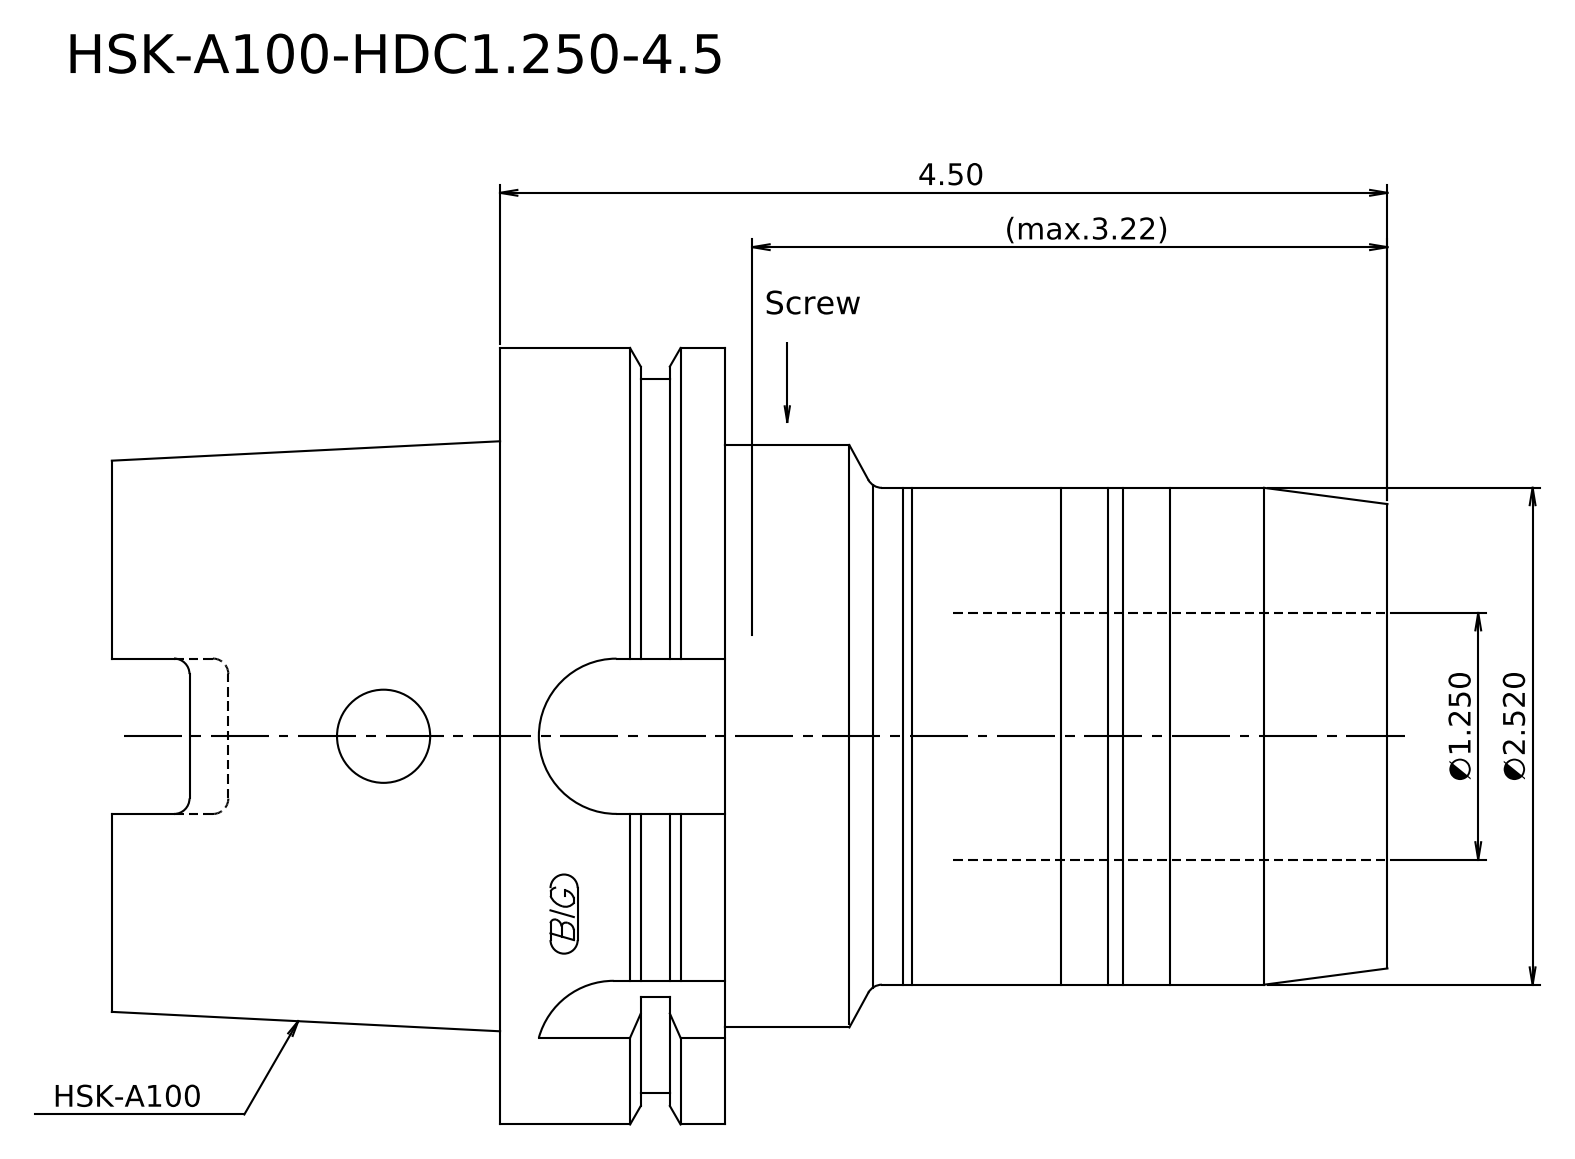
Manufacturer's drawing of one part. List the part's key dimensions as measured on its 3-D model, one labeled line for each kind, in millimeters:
STEP written by: Kubotek KeyCreator 2011 V10.0.2 (22737) (automotive_design)
Units: millimetres
Bodies: 1 solid, 16 faces (6 planar, 5 cylindrical, 5 other)
Overall size (bounding box): 164.3 × 100 × 100
Volume: 727 262 mm³ · Surface area: 54 168 mm²
Round bosses / shafts (diameter × count): ⌀100 ×1, ⌀92 ×1, ⌀75 ×1, ⌀64 ×1
Main face-to-face distances: 79, 29, 50, 85.3, 114.3, 164.3, 92.42, 7.12, 21.88, 71.88
